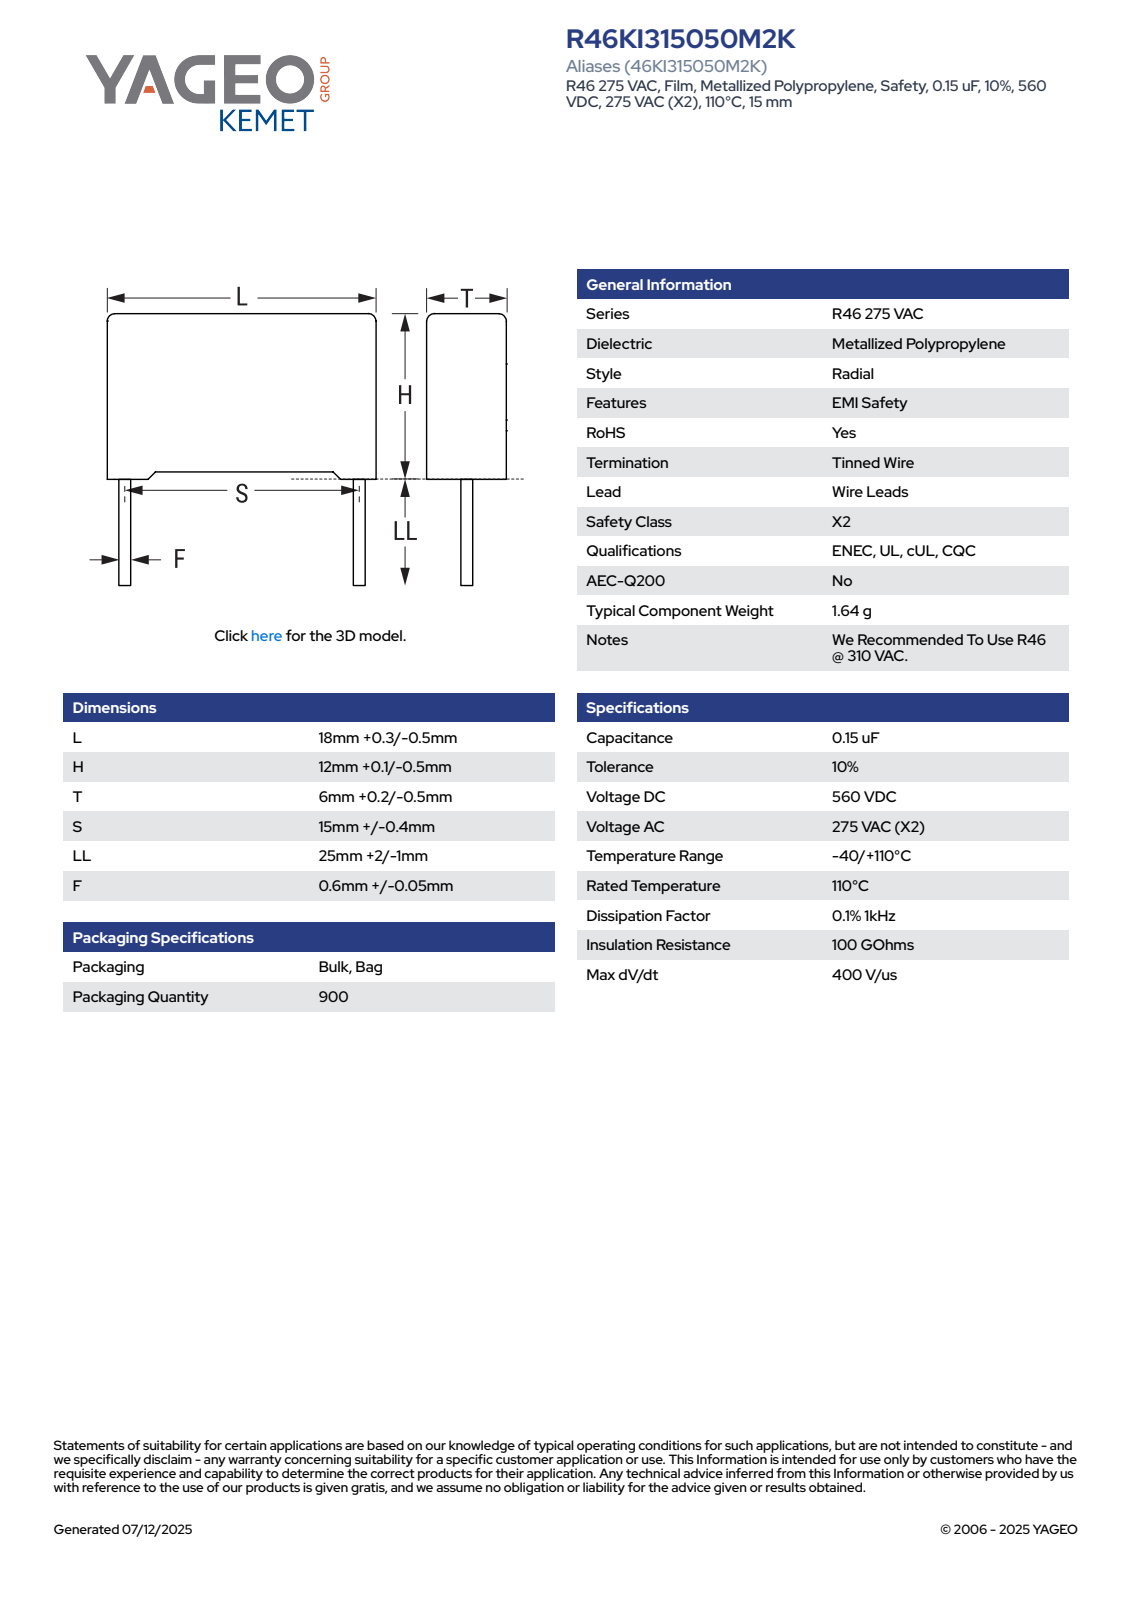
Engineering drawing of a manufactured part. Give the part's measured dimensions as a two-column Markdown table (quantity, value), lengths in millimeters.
| quantity | value |
| --- | --- |
| part name | CFR_RB2_18X12X6_L18.3H12.1T6.2S15LL27F0.65 |
| STEP written by | SolidWorks 2021 (AUTOMOTIVE_DESIGN) |
| units | millimeters |
| bodies | 4 solids, 85 faces (77 planar, 8 cylindrical, 0 other) |
| overall size | 39.1 × 18.3 × 6.21 |
| volume | 1 319 mm³ |
| surface area | 962 mm² |
| round bosses / shafts (diameter × count) | 0.65 × 2 |
| partial cylindrical surfaces (radius × count) | 0.5 × 4 |
| main face-to-face distances | 6.2, 11.35, 18.3, 0.61, 5.59, 0.75, 12.1, 0.42, 0.33, 11.68 |
